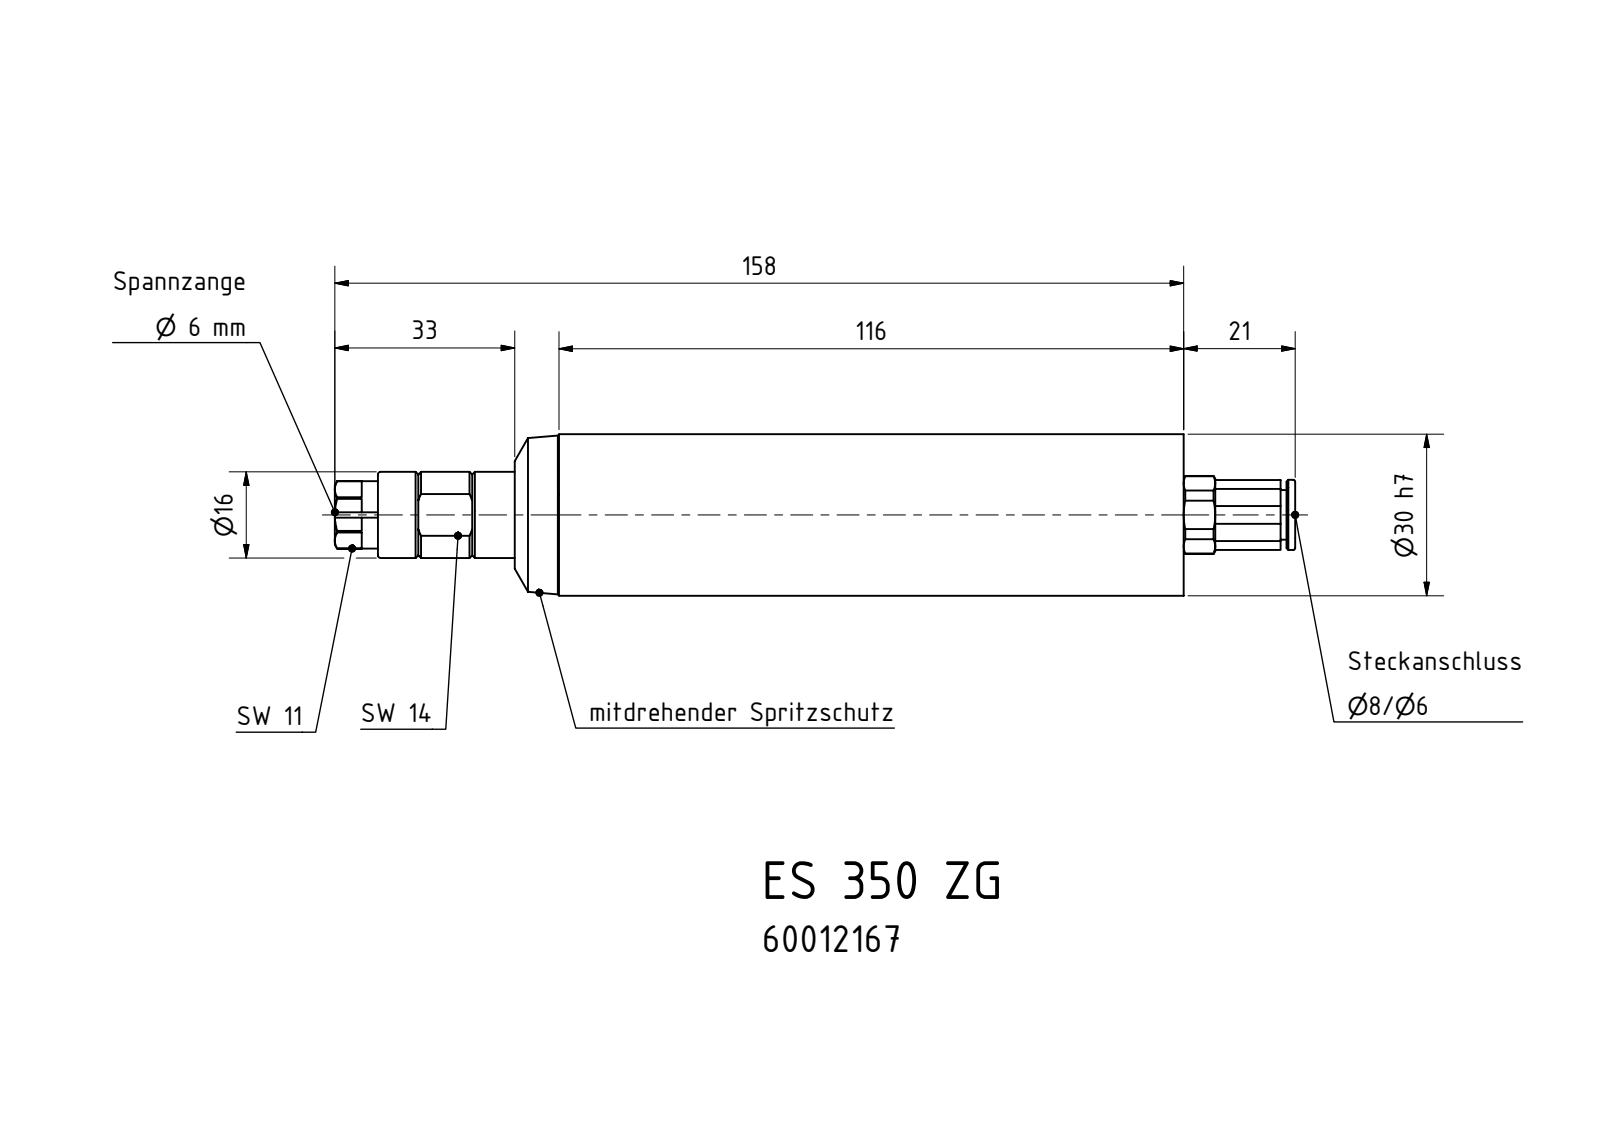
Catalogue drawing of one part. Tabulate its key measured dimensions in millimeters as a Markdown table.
| quantity | value |
| --- | --- |
| part name | ES 350 ER_60012167 |
| STEP written by | Autodesk Inventor 2008 (CONFIG_CONTROL_DESIGN) |
| units | millimeters |
| bodies | 1 solid, 170 faces (83 planar, 35 cylindrical, 52 other) |
| overall size | 178.3 × 30 × 30 |
| volume | 93 044 mm³ |
| surface area | 17 496 mm² |
| round holes (diameter × count) | 8 × 1, 9.18 × 1 |
| round bosses / shafts (diameter × count) | 30 × 1, 27.33 × 1, 16 × 1, 13 × 1, 12.5 × 1, 9.98 × 1, 9.2 × 1 |
| partial cylindrical surfaces (radius × count) | 50 × 3, 4.11 × 1, 6.75 × 1, 7.25 × 1 |
| main face-to-face distances | 6, 7, 1.25, 12.25, 8, 116, 3, 124.2, 8.2, 33.4 |
